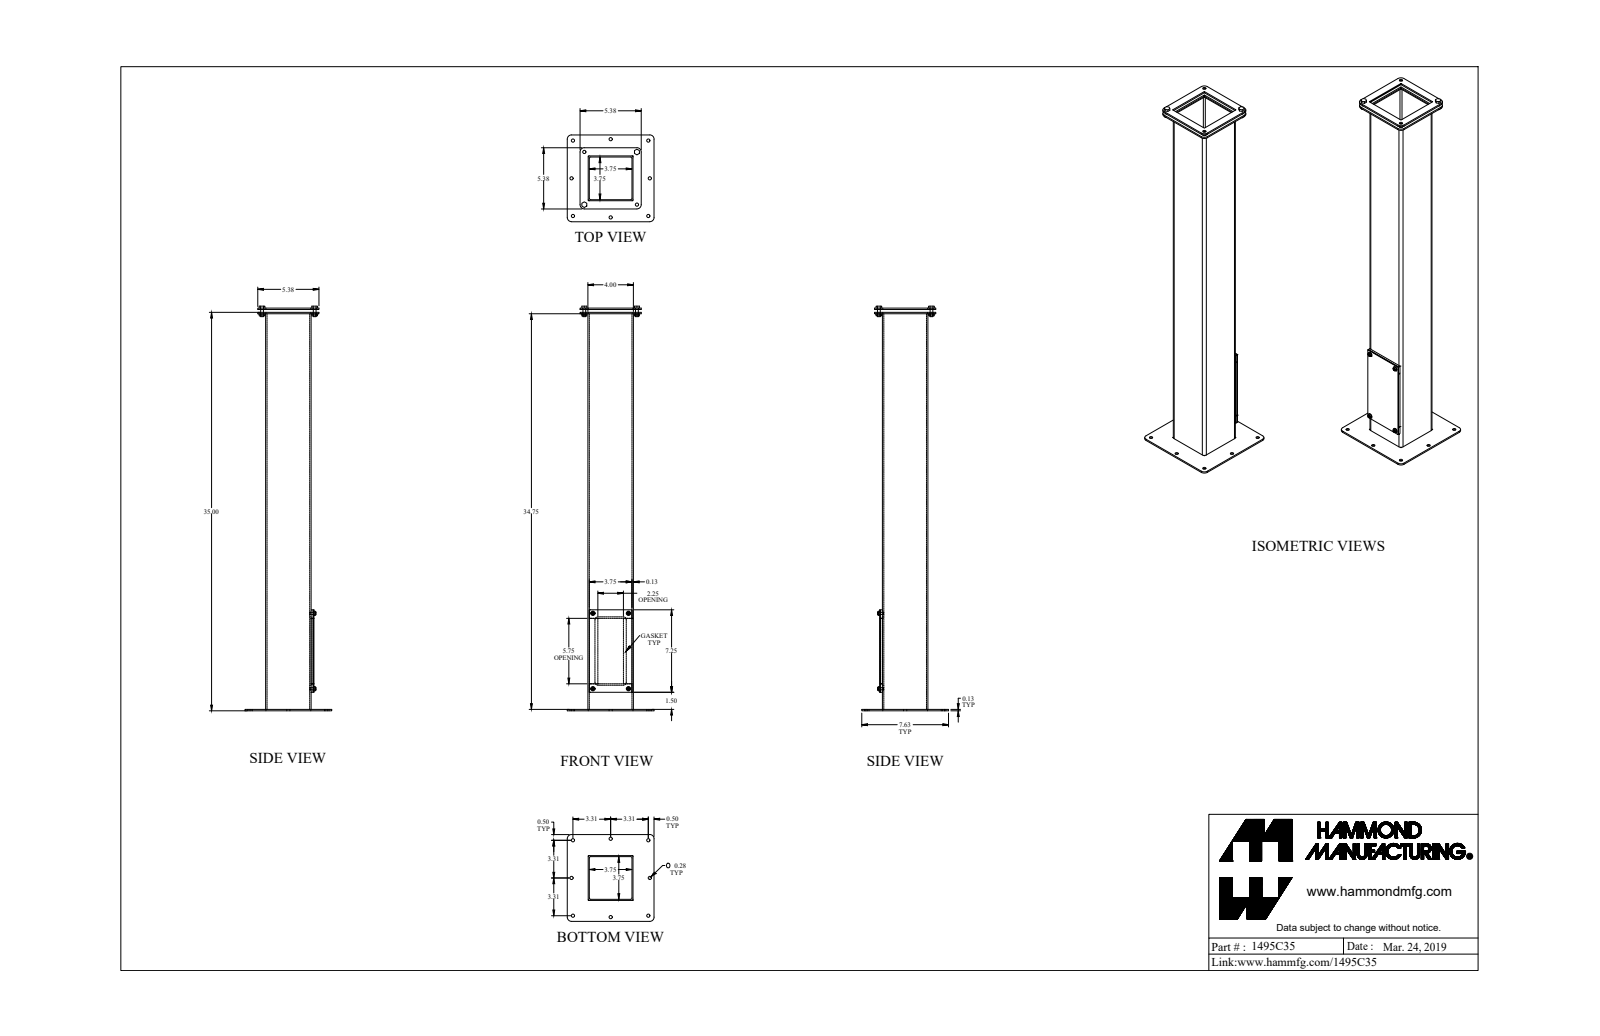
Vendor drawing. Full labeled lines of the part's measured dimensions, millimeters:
Part name (STEP PRODUCT): 1495C35_Default
STEP written by: SolidWorks 2019 (CONFIG_CONTROL_DESIGN)
Units: millimetres
Bodies: 17 solids, 350 faces (206 planar, 112 cylindrical, 32 other)
Overall size (bounding box): 902.9 × 193.7 × 193.7
Volume: 1 260 000 mm³ · Surface area: 825 200 mm²
Round holes (diameter × count): ⌀7.1 ×12, ⌀4 ×4, ⌀6.4 ×4, ⌀5 ×2
Round bosses / shafts (diameter × count): ⌀4.7 ×4, ⌀9.8 ×2, ⌀9.8 ×2, ⌀6.2 ×2
Partial cylindrical surfaces — rounded edges, fillets, slot ends (radius × count): R6.4 ×8, R9.5 ×8, R0.3 ×4, R3.2 ×4
Main face-to-face distances: 3.2, 3.2, 98.4, 101.6, 98.4, 95.3, 6.2, 9.4, 104.6, 107.8
Hole centre spacings: 157.4, 191, 65.3, 84.2, 168.3, 35.9, 145.1, 145.1
